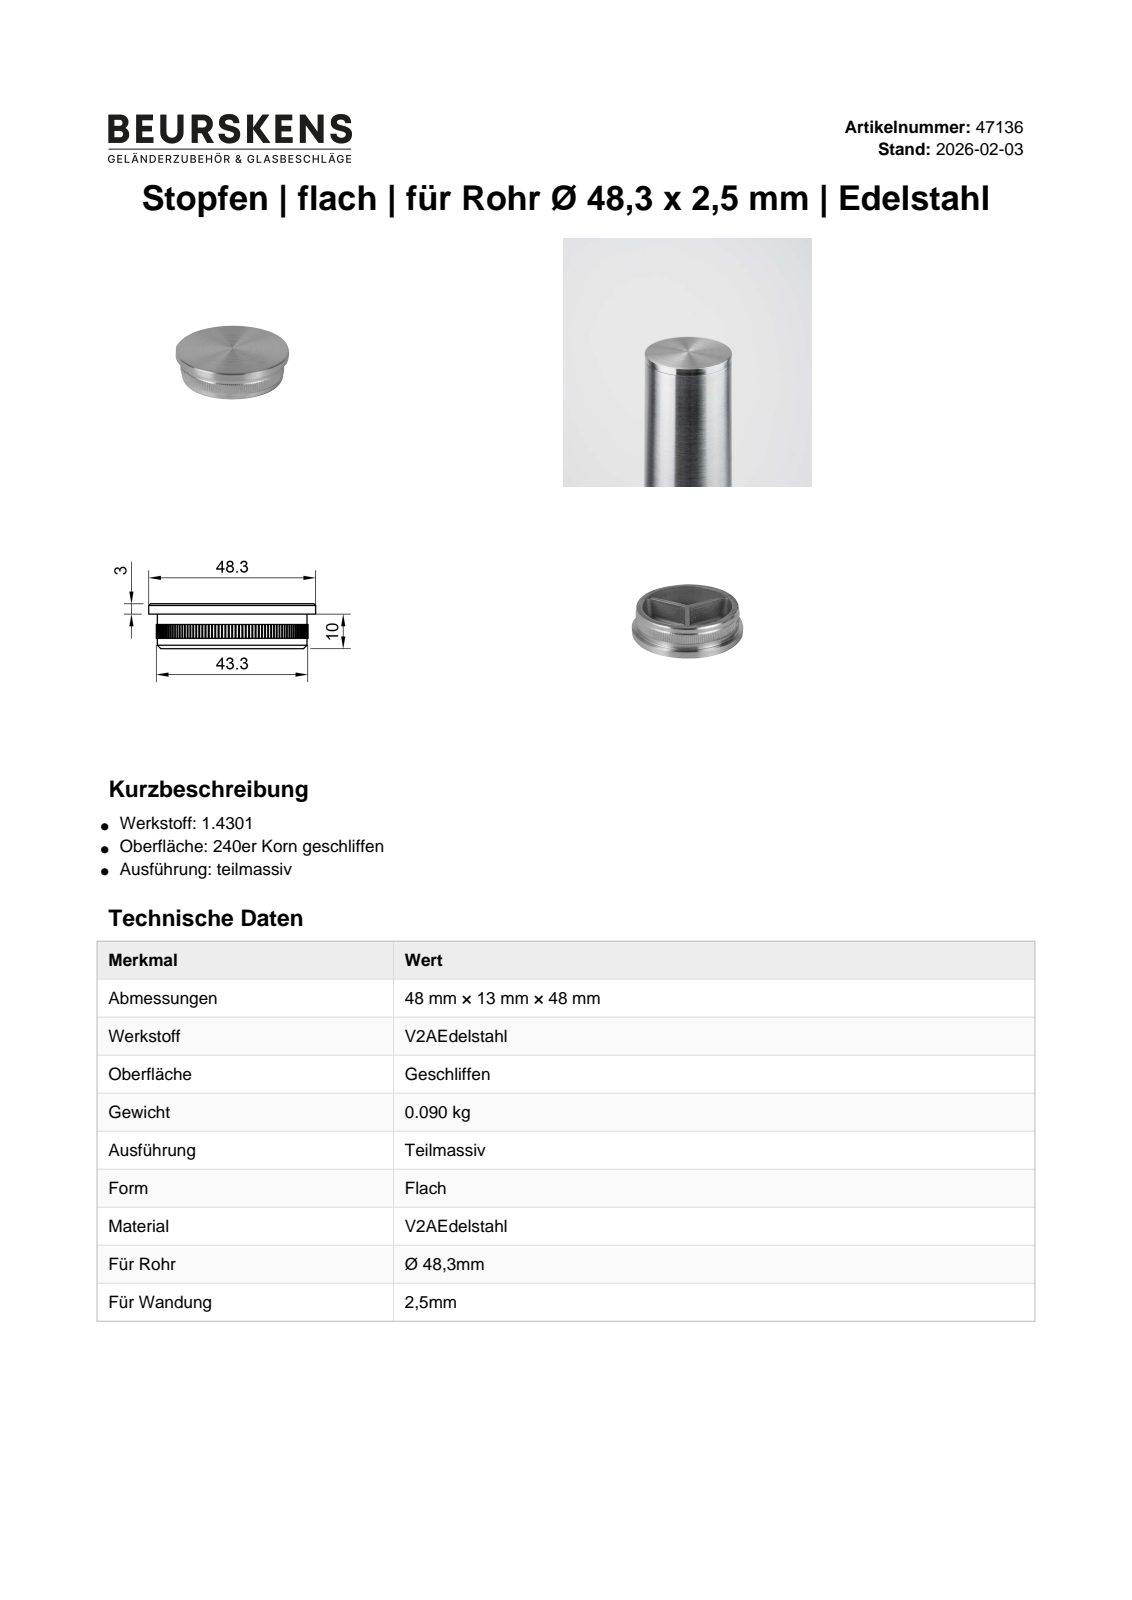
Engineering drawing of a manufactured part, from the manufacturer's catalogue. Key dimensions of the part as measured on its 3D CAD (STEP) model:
Part name (STEP PRODUCT): 47136
STEP written by: Autodesk Inventor 2022 (AUTOMOTIVE_DESIGN)
Units: millimetres
Bodies: 1 solid, 292 faces (6 planar, 284 cylindrical, 2 other)
Overall size (bounding box): 48.3 × 48.3 × 13
Volume: 8 946 mm³ · Surface area: 6 710 mm²
Round holes (diameter × count): ⌀38 ×1
Round bosses / shafts (diameter × count): ⌀48.3 ×1, ⌀43.3 ×1
Partial cylindrical surfaces — rounded edges, fillets, slot ends (radius × count): R0.12 ×140, R21.95 ×1
Main face-to-face distances: 3, 10, 13, 7, 4, 6
